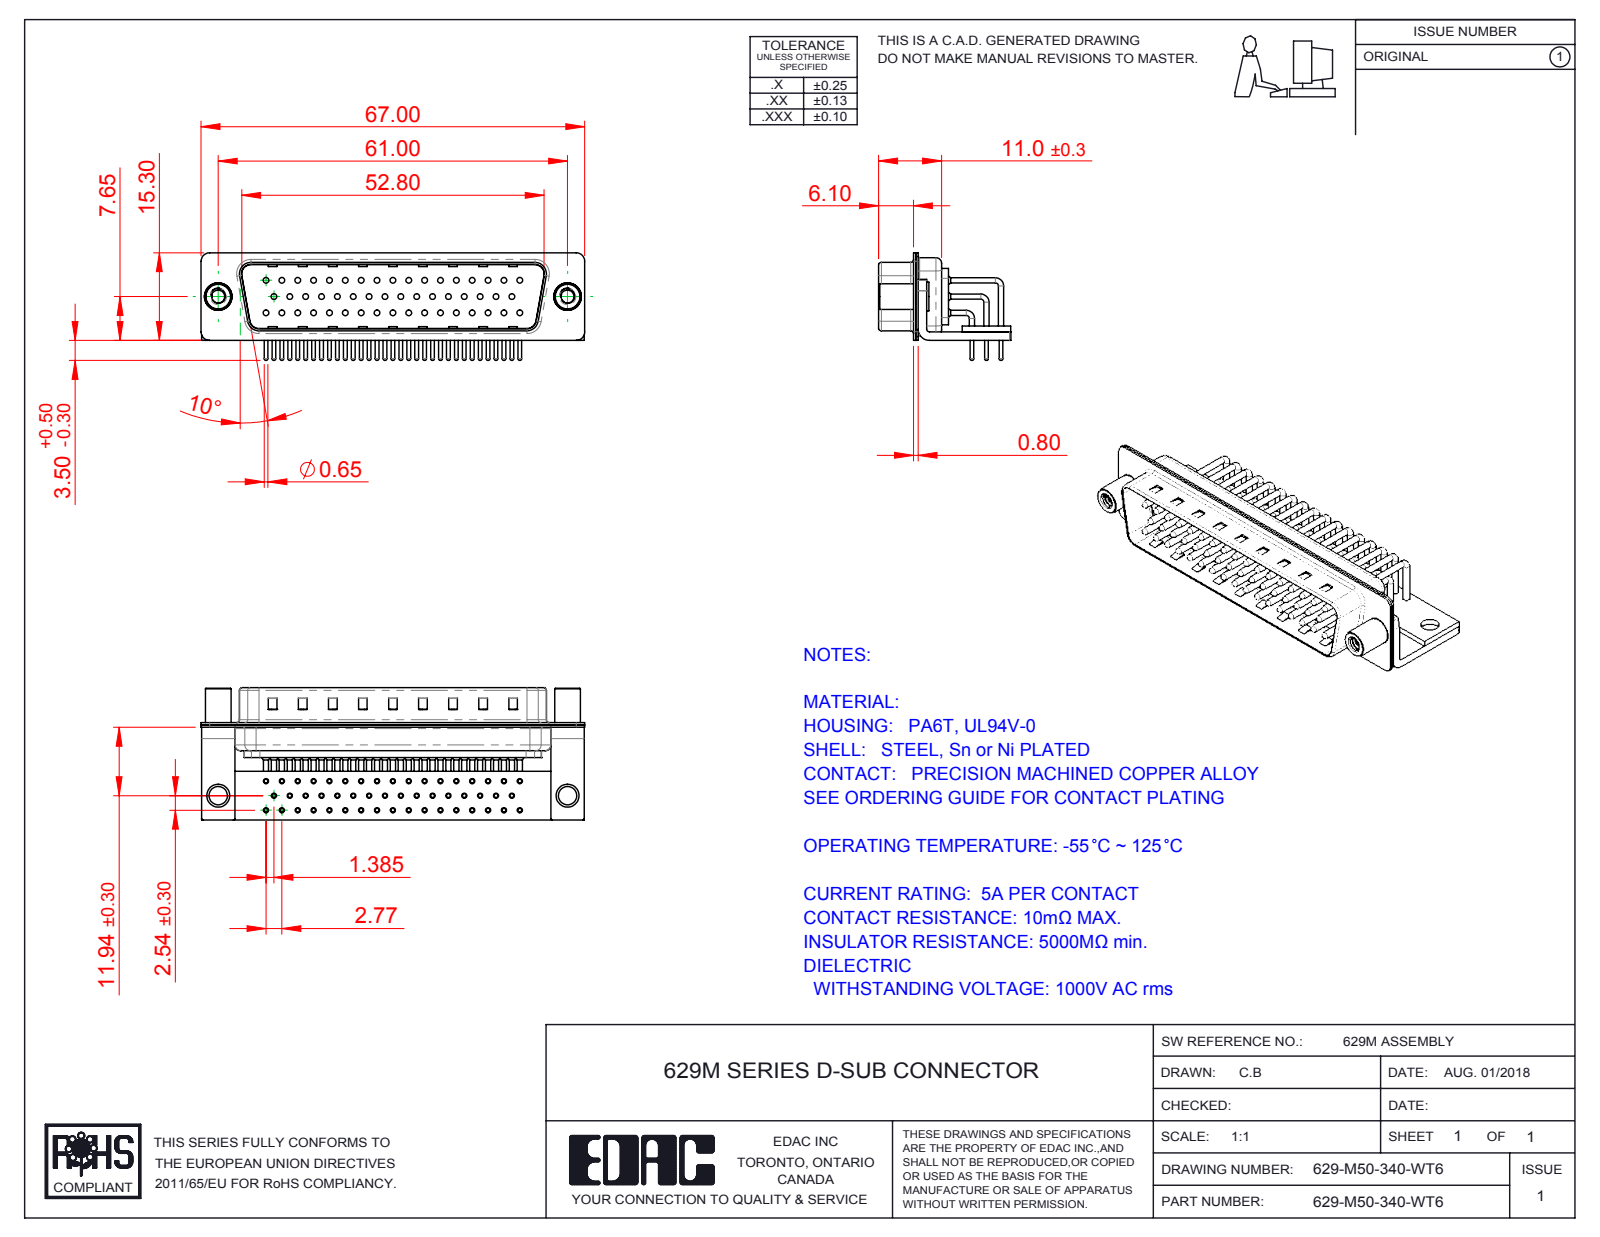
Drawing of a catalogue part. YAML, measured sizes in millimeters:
part_name: "629M Shell Front_50 Contacts; 629M Contact Row 3; 629M Stabilizer Bracket_50 Contacts; 629-M50-340-WT6 (+6 more)"
step_written_by: "SolidWorks 2016 (CONFIG_CONTROL_DESIGN)"
units: millimeters
bodies: {solids: 58, faces: 6112, planar: 3431, cylindrical: 2105, other: 576}
overall_size: [67, 23.1, 18.8]
volume: 5961
surface_area: 15252
round_holes:
  - {diameter: 0.9, count: 50}
  - {diameter: 1, count: 50}
  - {diameter: 1.7, count: 50}
  - {diameter: 2, count: 50}
  - {diameter: 2.26, count: 2}
  - {diameter: 3.2, count: 2}
  - {diameter: 4, count: 2}
  - {diameter: 4.8, count: 2}
round_bosses_or_shafts:
  - {diameter: 0.9, count: 58}
  - {diameter: 1.5, count: 50}
  - {diameter: 0.65, count: 50}
  - {diameter: 5, count: 2}
  - {diameter: 4.9, count: 2}
  - {diameter: 4.5, count: 2}
partial_cylinders:
  - {radius: 1.01, count: 50}
  - {radius: 0.25, count: 16}
  - {radius: 1.5, count: 16}
  - {radius: 2, count: 13}
  - {radius: 0.5, count: 9}
  - {radius: 1.6, count: 8}
  - {radius: 0.6, count: 4}
  - {radius: 0.65, count: 4}
face_to_face_distances: [0.4, 1, 11.55, 1.5, 0.83, 5.7, 0.43, 11.95, 1.9, 0.8]
hole_center_spacings: [2.77, 5.54, 8.31, 11.08, 13.85, 16.62, 3.16, 19.39]
